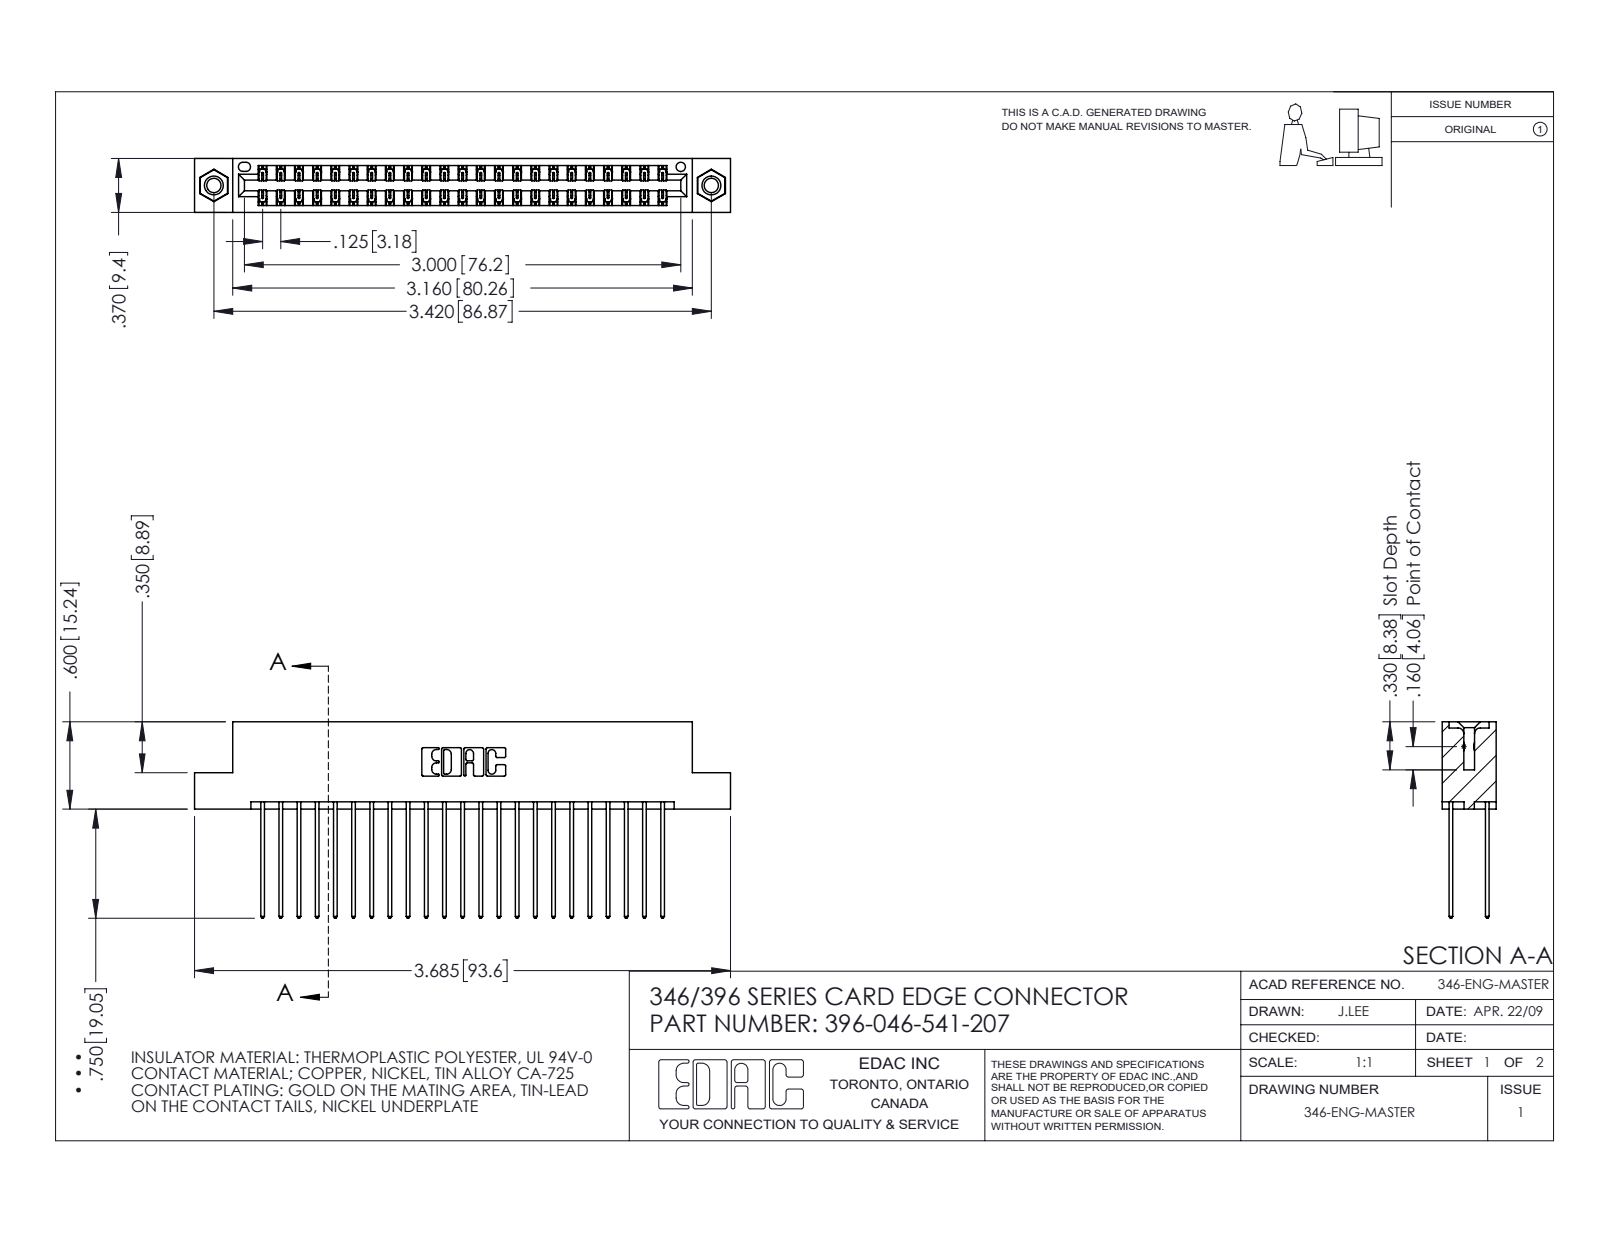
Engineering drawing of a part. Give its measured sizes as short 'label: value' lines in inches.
name: 396-046-541-207; 345-292-001_345-293-141; 346 Part_Flush Mounting Lugs - 0.156 Dia-TI; 345-250-001_345-250-005-103
written by: SolidWorks 2016 (CONFIG_CONTROL_DESIGN)
unit: in
bodies: 49 solids, 2574 faces (1718 planar, 840 cylindrical, 16 other)
size: 3.685 × 1.35 × 0.37
volume: 0.563 in³; area: 21.22 in²
holes: 2× ⌀0.098, 2× ⌀0.125, 2× ⌀0.156, 1× ⌀0.064
bosses: 2× ⌀0.155
rounds: 69× R0.006, 46× R0.01, 22× R0.01, 6× R0.007, 6× R0.031, 3× R0.026, 2× R0.014, 2× R0.022
face distances: 0.048, 0.322, 0.25, 0.072, 0.298, 0.025, 0.37, 0.275, 0.148, 0.222
hole spacings: 0.246, 3.212, 3.42
